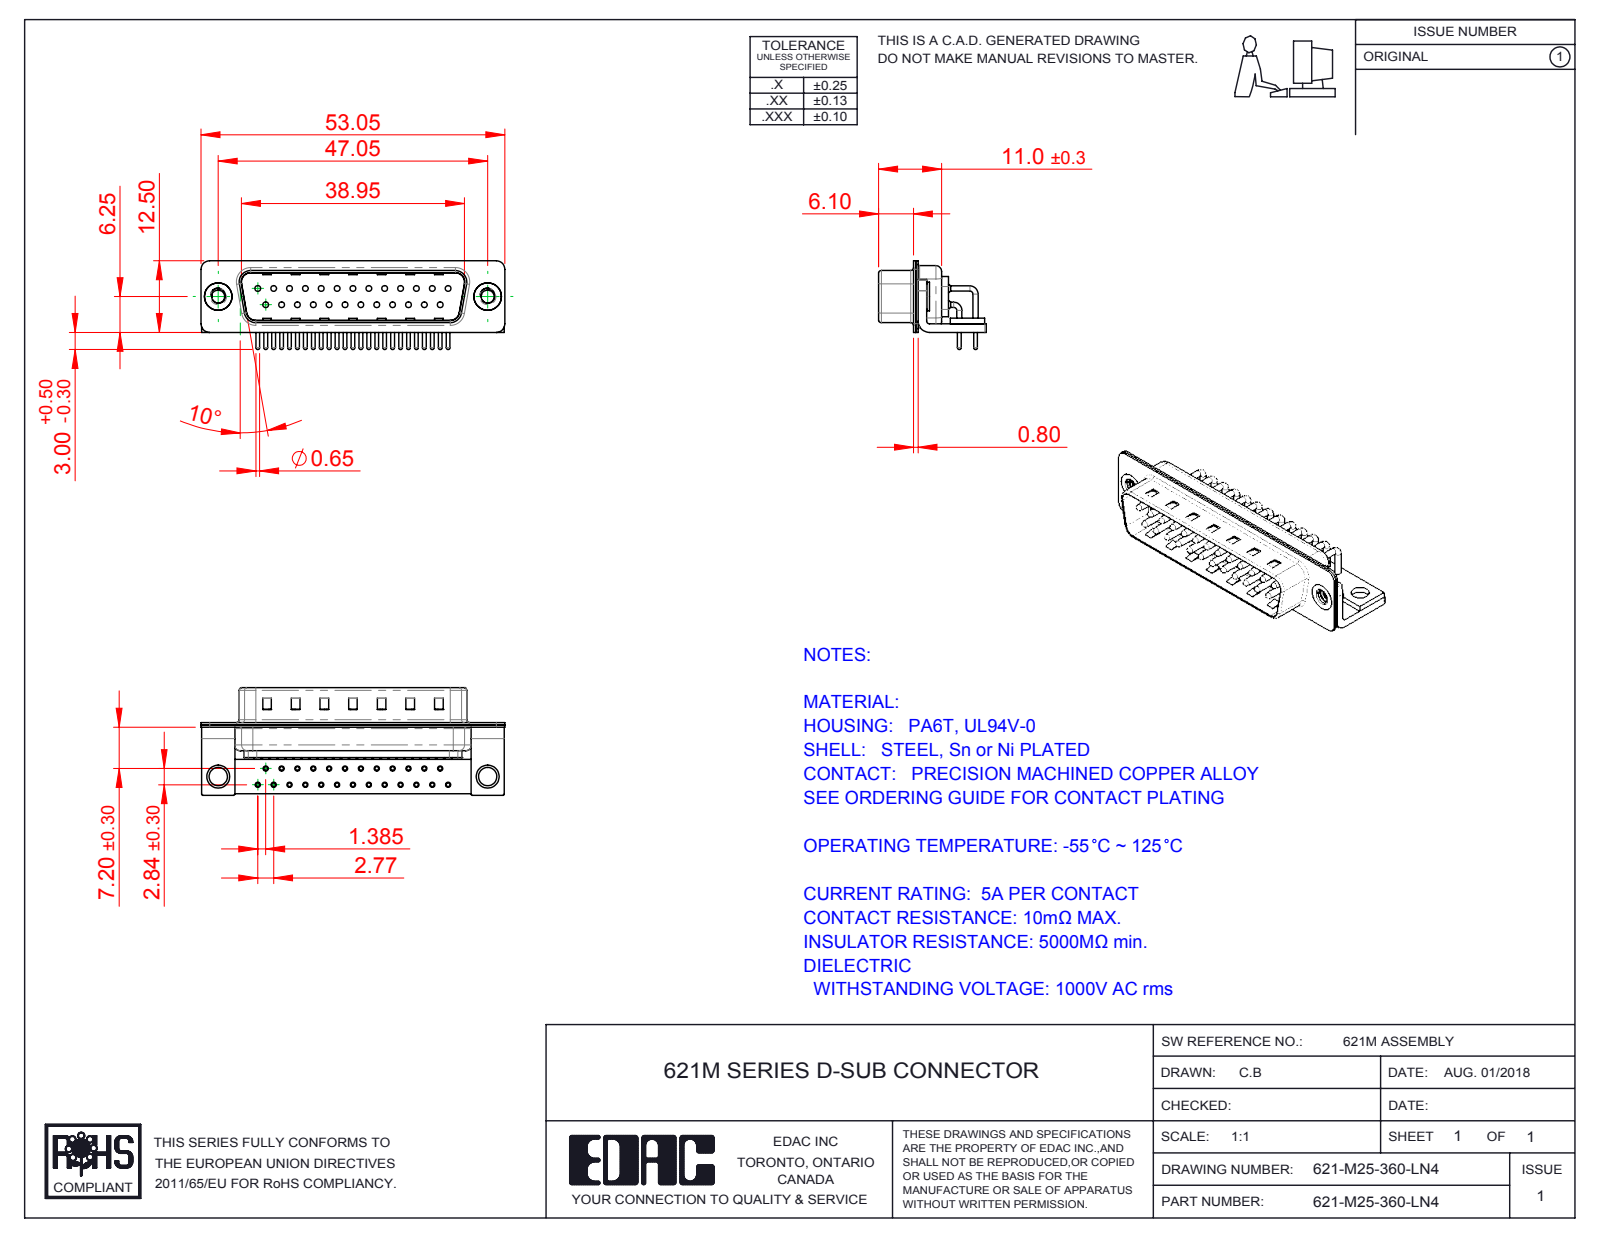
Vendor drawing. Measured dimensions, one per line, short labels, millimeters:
name: 621M Stabilizer Bracket; 621M Stabilizer Board_25 Contacts; 621M Shell Rear_25 Contacts; 621-M25-360-LN4 (+5 more)
written by: SolidWorks 2016 (CONFIG_CONTROL_DESIGN)
unit: mm
bodies: 33 solids, 3226 faces (1797 planar, 1109 cylindrical, 320 other)
size: 53.05 × 18.8 × 15.49
volume: 3 385 mm³; area: 8 887 mm²
holes: 25× ⌀0.9, 25× ⌀1, 25× ⌀1.7, 25× ⌀2, 2× ⌀2.26, 2× ⌀3.2, 2× ⌀4, 2× ⌀4.8
bosses: 33× ⌀0.9, 25× ⌀1.5, 25× ⌀0.65, 2× ⌀5, 2× ⌀4.9
rounds: 25× R1.01, 16× R0.25, 16× R1.5, 13× R2, 9× R0.5, 8× R1.6, 4× R0.6, 4× R0.65
face distances: 0.4, 0.85, 1.25, 1.5, 9.55, 0.8, 10.4, 1, 8.3, 8.7
hole spacings: 3.16, 2.77, 8.31, 5.54, 11.08, 13.85, 5.04, 16.62
